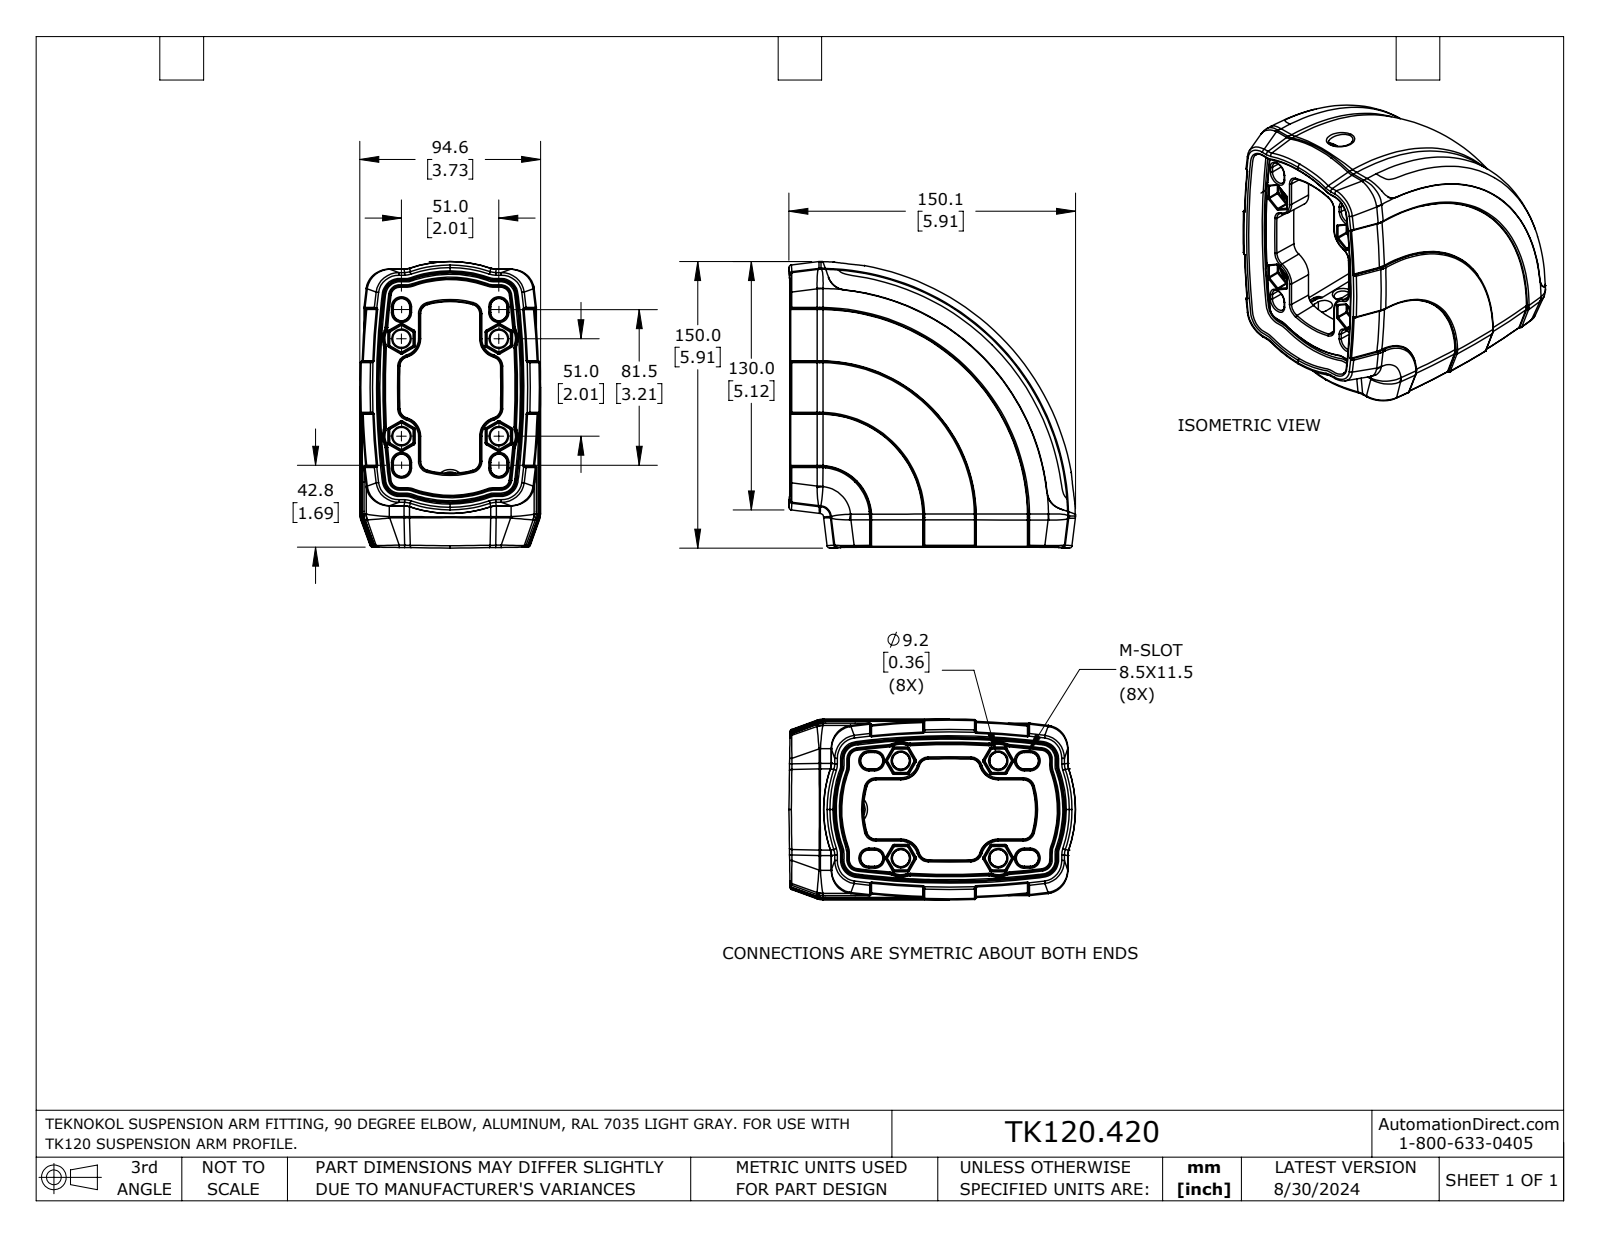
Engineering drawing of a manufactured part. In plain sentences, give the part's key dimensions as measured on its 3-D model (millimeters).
The part is named "TK120.420". Its 3-D file was written by "SolidWorks 2023 (AUTOMOTIVE_DESIGN)". It is 4 solids with 1485 faces: 136 planar, 256 cylindrical and 1093 other. Overall it measures 150.1 by 150.1 by 94.6 millimeters. Its volume is 492 300 cubic millimeters and its surface area 141 200 square millimeters. Round holes: 4 of diameter 9.2. Round bosses or shafts: 2 of diameter 10, 1 of diameter 6, 1 of diameter 6. Partial cylindrical surfaces (rounded edges, fillets, slot ends): 128 of radius 0.5, 14 of radius 0.8, 12 of radius 0.1, 12 of radius 2.7, 8 of radius 1.4, 4 of radius 3, 4 of radius 9, 2 of radius 2. The main face-to-face distances are 13, 1.5, 11.5, 13.3, 25.5, 51, 44.2, 7, 5.5, 6. The hole center spacings are 51, 72.1.
